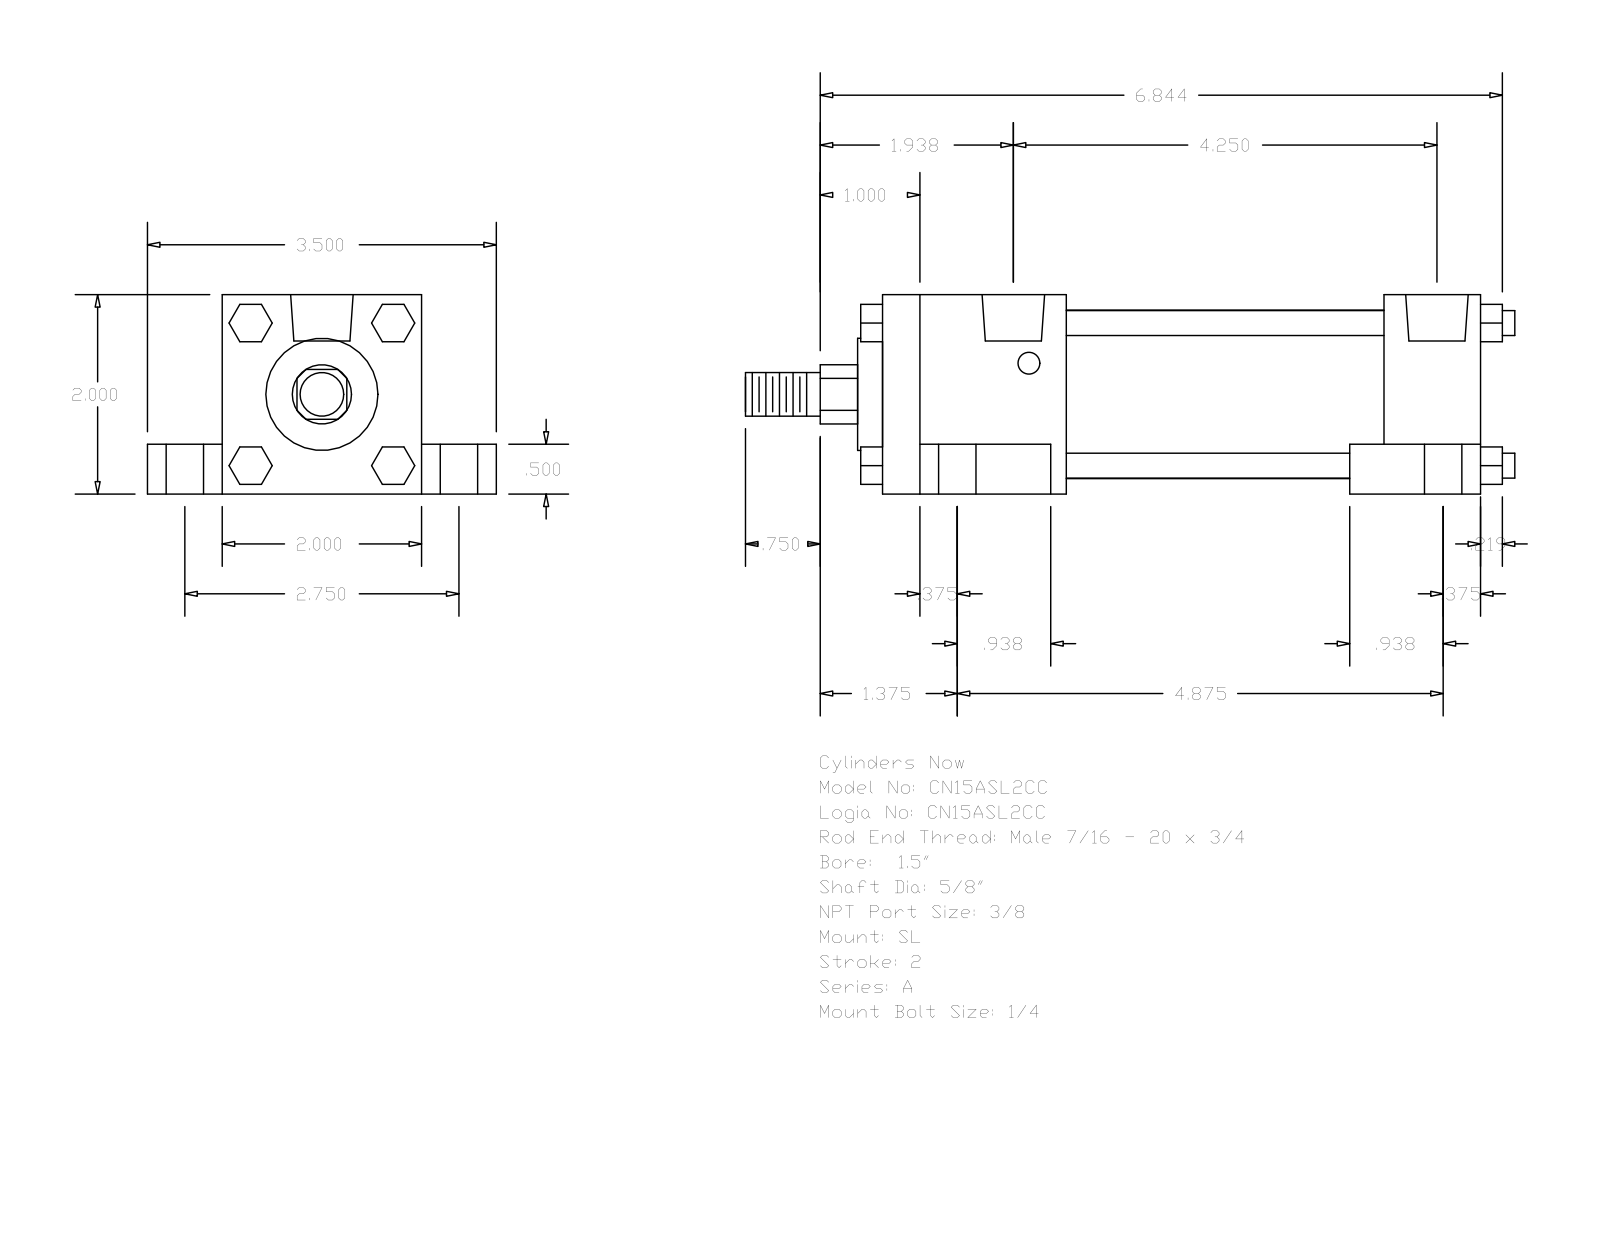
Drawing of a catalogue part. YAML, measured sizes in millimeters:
part_name: "A_SL__0150_0.625"
step_written_by: "GSSL Pune (CONFIG_CONTROL_DESIGN)"
units: millimeters
bodies: {solids: 0, faces: 148, planar: 112, cylindrical: 36, other: 0}
overall_size: [196.06, 88.9, 50.8]
round_holes:
  - {diameter: 5.56, count: 4}
  - {diameter: 9.53, count: 4}
  - {diameter: 15.88, count: 4}
  - {diameter: 15.93, count: 2}
round_bosses_or_shafts:
  - {diameter: 6.35, count: 4}
  - {diameter: 42.93, count: 1}
  - {diameter: 28.57, count: 1}
  - {diameter: 15.88, count: 1}
  - {diameter: 11.11, count: 1}
partial_cylinders:
  - {radius: 7.54, count: 1}
face_to_face_distances: [50.8, 19.05, 38.1, 12.7, 69.85, 152.4, 9.52, 33.34, 127.79, 24.61]
hole_center_spacings: [3.97, 34.96, 35.36, 37.73, 39.41, 69.84, 100.01, 103.98]
